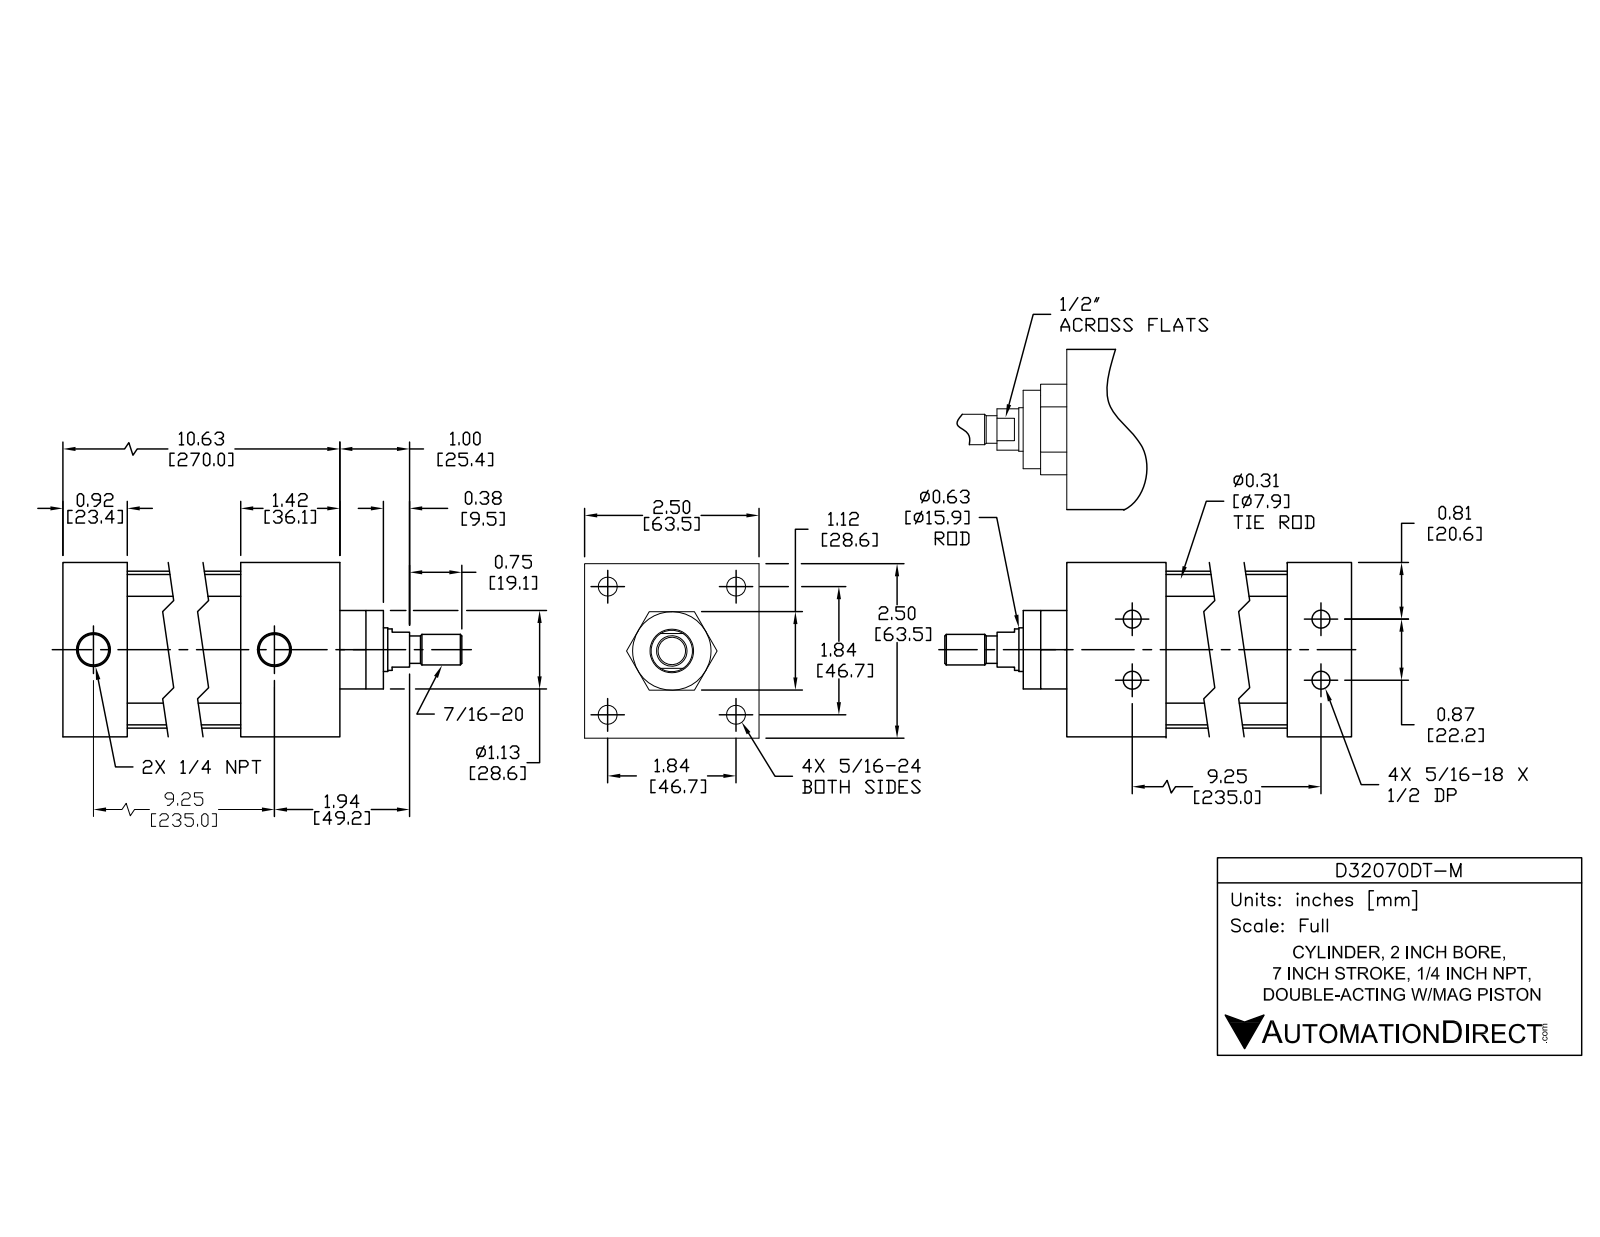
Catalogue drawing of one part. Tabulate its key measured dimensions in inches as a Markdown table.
| quantity | value |
| --- | --- |
| part name | D32070DT-M; D32070DT-M PISTON; D32070DT-M BODY |
| STEP written by | SolidWorks 2015 (AUTOMOTIVE_DESIGN) |
| units | inches |
| bodies | 12 solids, 298 faces (94 planar, 114 cylindrical, 90 other) |
| overall size | 12.371 × 2.5 × 2.5 |
| volume | 29.55 in³ |
| surface area | 255.5 in² |
| round holes (diameter × count) | 0.252 × 4, 0.267 × 4, 0.359 × 4, 0.5 × 4, 0.297 × 2, 0.477 × 2, 0.625 × 1, 0.628 × 1, 2 × 1 |
| round bosses / shafts (diameter × count) | 0.484 × 4, 0.313 × 4, 0.282 × 4, 2.25 × 1, 1.997 × 1, 1.12 × 1, 0.622 × 1, 0.59 × 1 |
| partial cylindrical surfaces (radius × count) | 0.25 × 4 |
| main face-to-face distances | 2.5, 10.621, 1.42, 9.201, 9.701, 8.281, 0.92, 1, 9.601, 8.181 |
| hole center spacings | 0.437, 1.307, 1.848, 9.255, 9.245, 0.875, 2.613, 9.286 |
